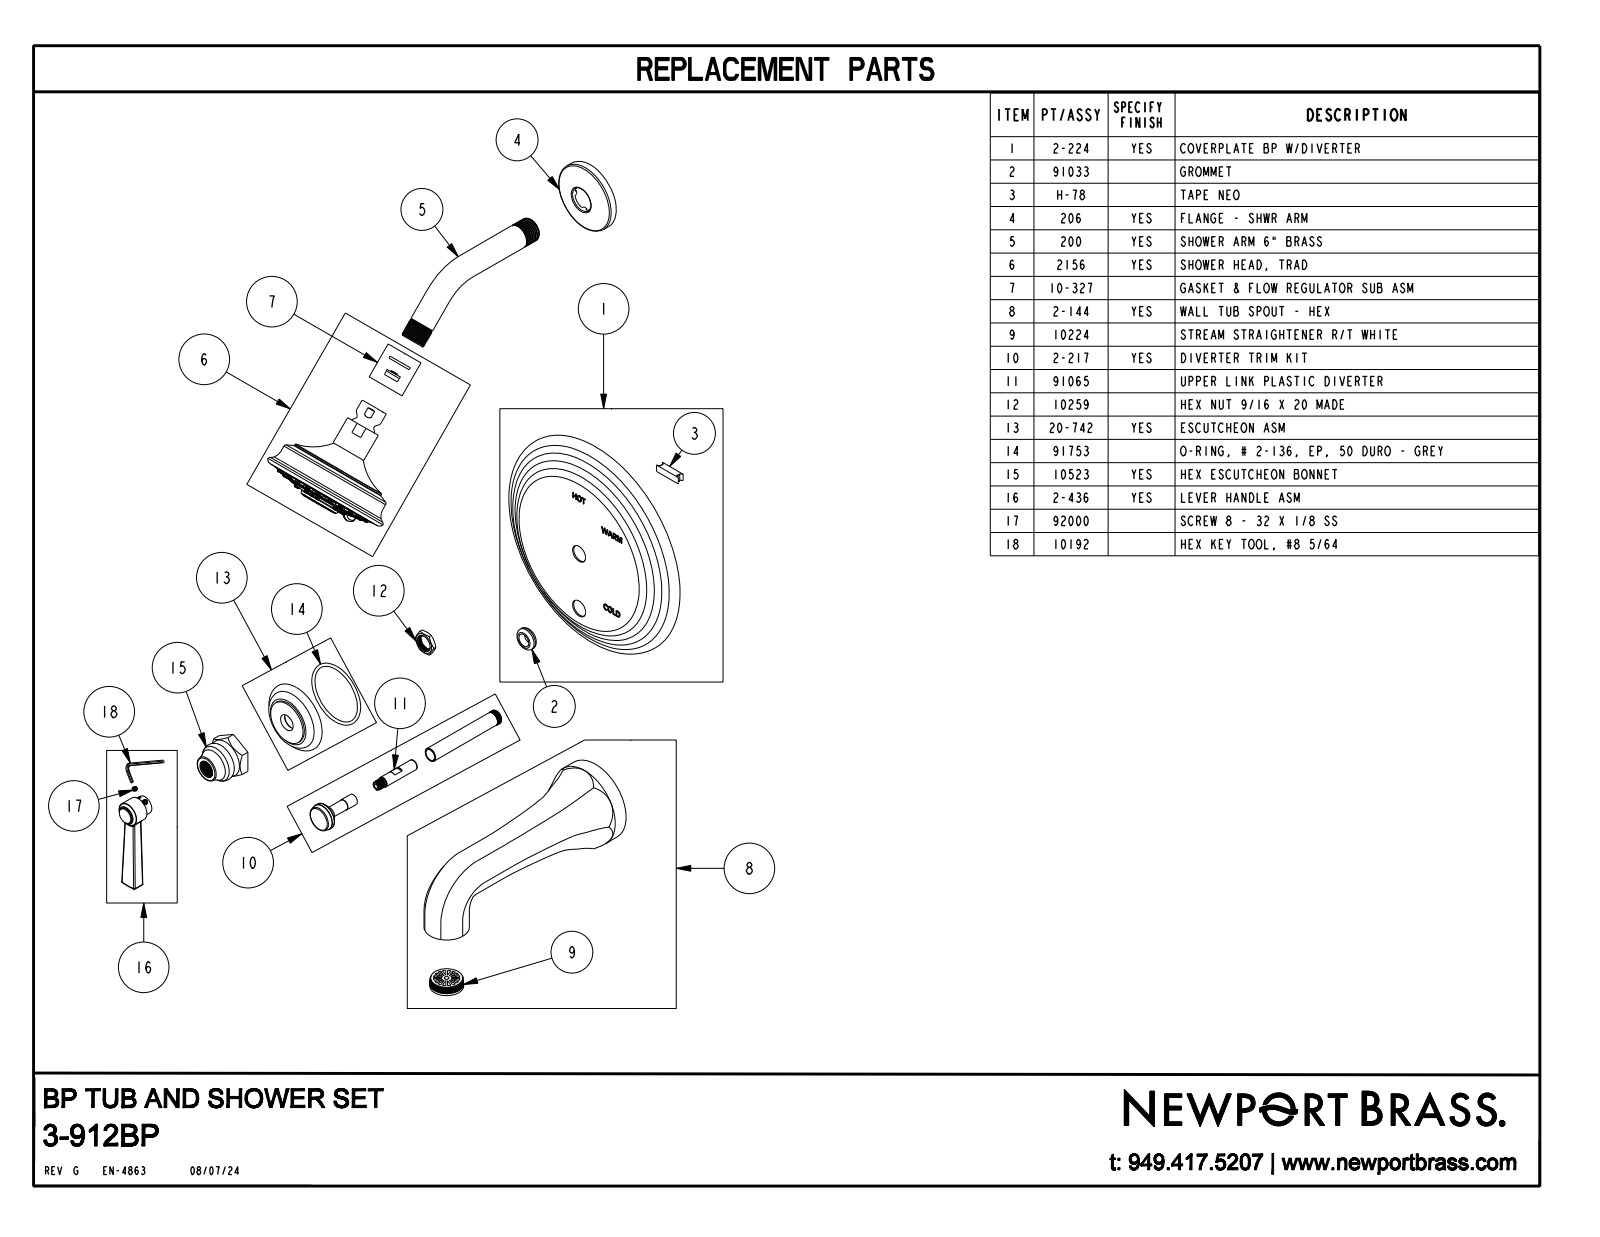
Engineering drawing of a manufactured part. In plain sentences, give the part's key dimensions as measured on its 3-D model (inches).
The part is named "3-912BP". Its 3-D file was written by "CREO PARAMETRIC BY PTC INC, 2018400 (CONFIG_CONTROL_DESIGN)". It is 3 solids with 1397 faces: 268 planar, 224 cylindrical and 905 other. Overall it measures 24.835 by 8.25 by 7.75 inches. Its volume is 70.31 cubic inches and its surface area 244.7 square inches. Round holes: 8 of diameter 0.059, 1 of diameter 0.925. Round bosses or shafts: 39 of diameter 0.142, 23 of diameter 0.165, 2 of diameter 0.813, 1 of diameter 3.81, 1 of diameter 3.724, 1 of diameter 3.24, 1 of diameter 2.8, 1 of diameter 2.38. Partial cylindrical surfaces (rounded edges, fillets, slot ends): 8 of radius 0.079, 6 of radius 2.125, 2 of radius 0.02, 2 of radius 0.04, 2 of radius 0.055, 1 of radius 0.138, 1 of radius 0.472, 1 of radius 0.512. The main face-to-face distances are 0.754, 1.299, 0.995, 2.294, 0.063, 0.118, 0.181, 1.313, 1.927, 1.173. The hole center spacings are 0.443, 0.579, 1.069, 0.819, 0.818, 1.157, 1.157.
